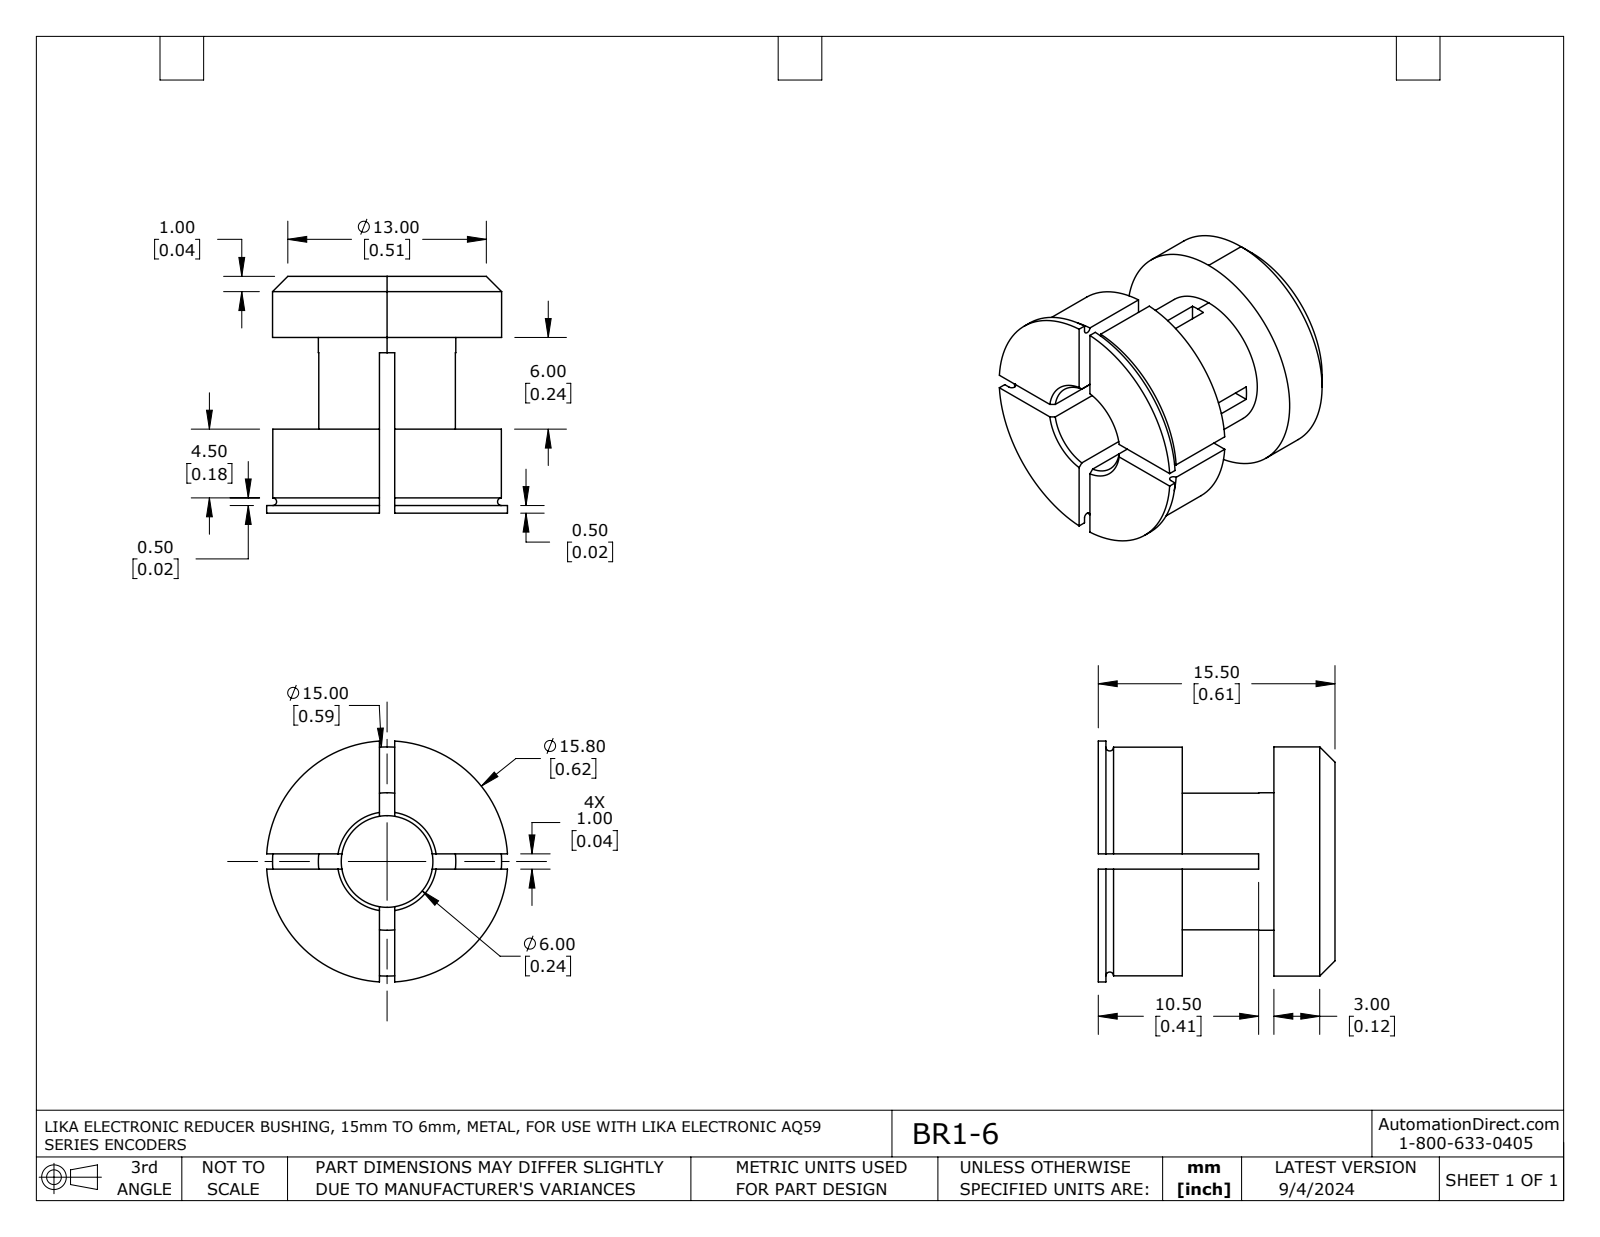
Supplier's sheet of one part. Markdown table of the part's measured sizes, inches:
| quantity | value |
| --- | --- |
| part name | BR1-6 |
| STEP written by | SolidWorks 2021 (AUTOMOTIVE_DESIGN) |
| units | inches |
| bodies | 1 solid, 54 faces (26 planar, 17 cylindrical, 11 other) |
| overall size | 0.621 × 0.621 × 0.61 |
| volume | 0.09 in³ |
| surface area | 2.483 in² |
| round holes (diameter × count) | 0.236 × 1 |
| round bosses / shafts (diameter × count) | 0.622 × 1, 0.591 × 1, 0.354 × 1 |
| main face-to-face distances | 0.039, 0.453, 0.394, 0.157, 0.61, 0.236, 0.217, 0.197, 0.591, 0.433 |
